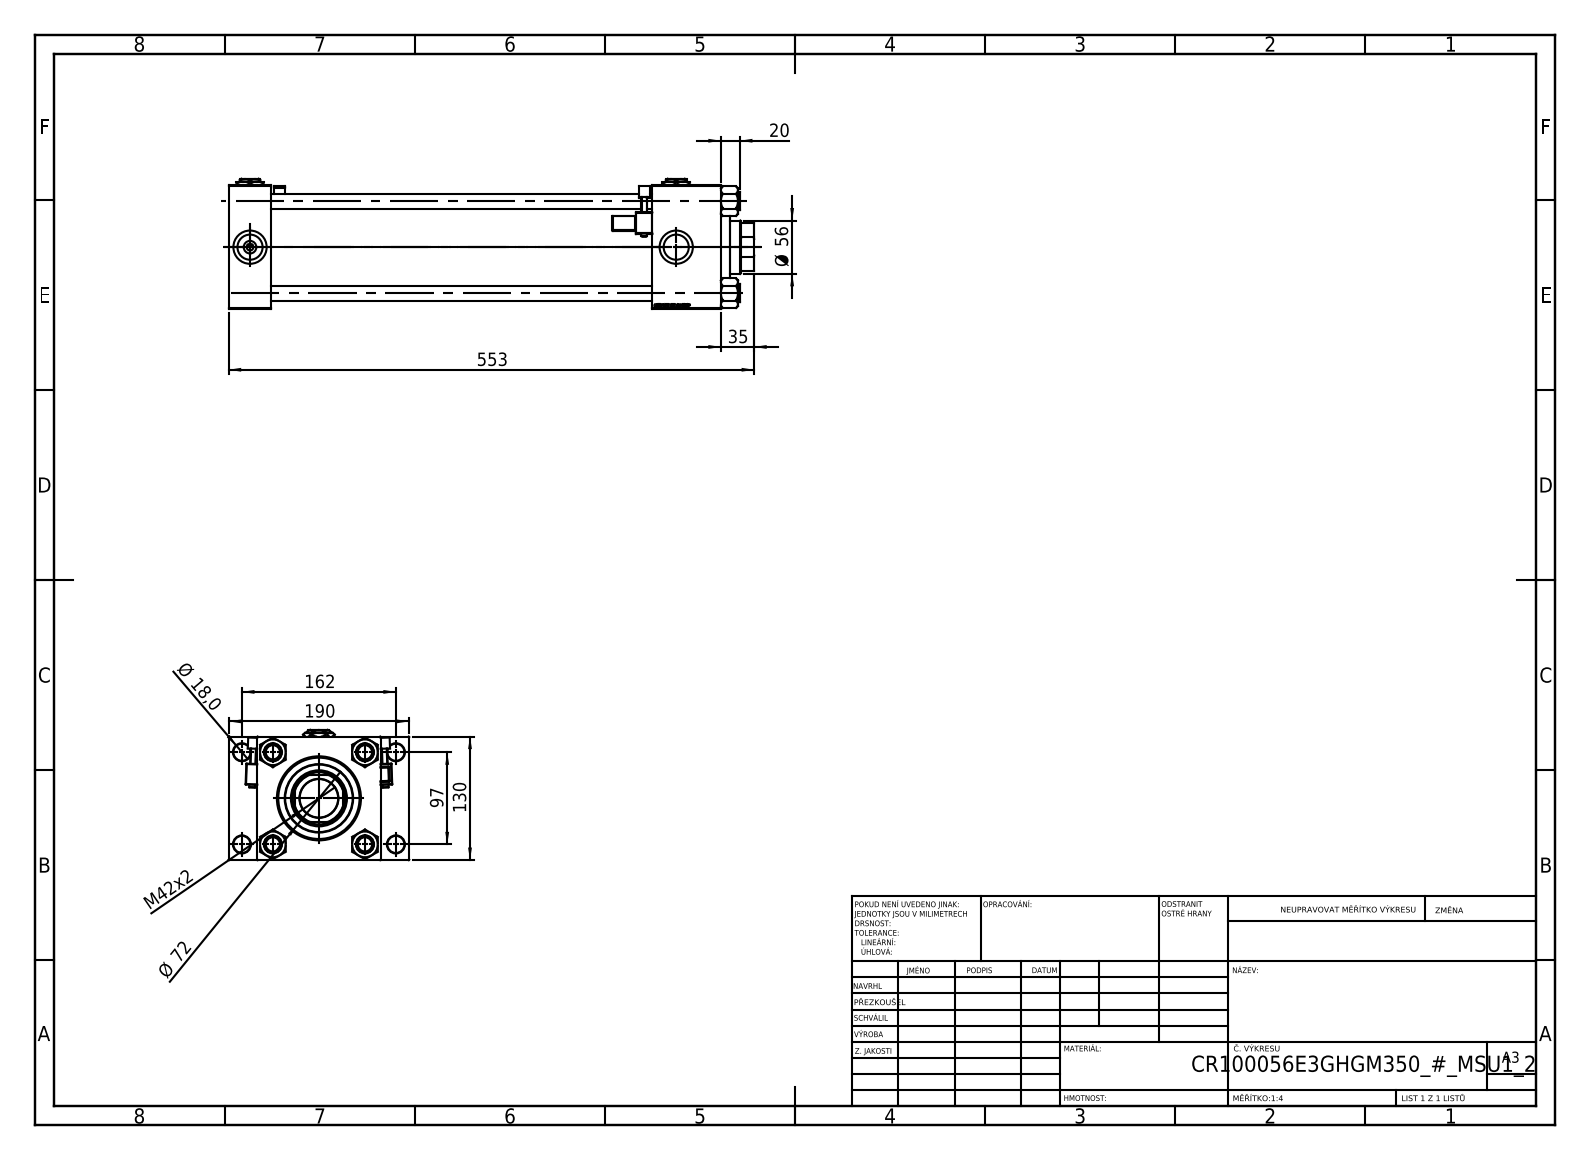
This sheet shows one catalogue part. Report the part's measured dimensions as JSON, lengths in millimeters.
{"part_name": "V215CR_TYCINKA_E; V215_VC_A; V215CR_MSU; V215CR_E_Body (+3 more)", "step_written_by": "SolidWorks 2019 (CONFIG_CONTROL_DESIGN)", "units": "millimeters", "bodies": {"solids": 15, "faces": 1438, "planar": 651, "cylindrical": 157, "other": 630}, "overall_size": [553, 190, 137], "volume_mm3": 4220000, "surface_area_mm2": 734733, "round_holes": [[16, 4], [18, 4], [26.44, 4], [35, 4], [7, 3], [40.5, 1], [56, 1], [59, 1], [76, 1], [85.5, 1], [100, 1]], "round_bosses_or_shafts": [[19, 4], [6, 2], [106, 1], [72, 1]], "partial_cylinders_radius": [[0.5, 48], [1, 2], [2.5, 2], [4, 2], [27, 1]], "face_to_face_distances": [130, 45, 518, 473, 30, 446, 401, 72, 160, 96], "hole_center_spacings": [32.55, 68.52, 94.41, 96.9, 102.27, 129.45, 161.73, 97]}
